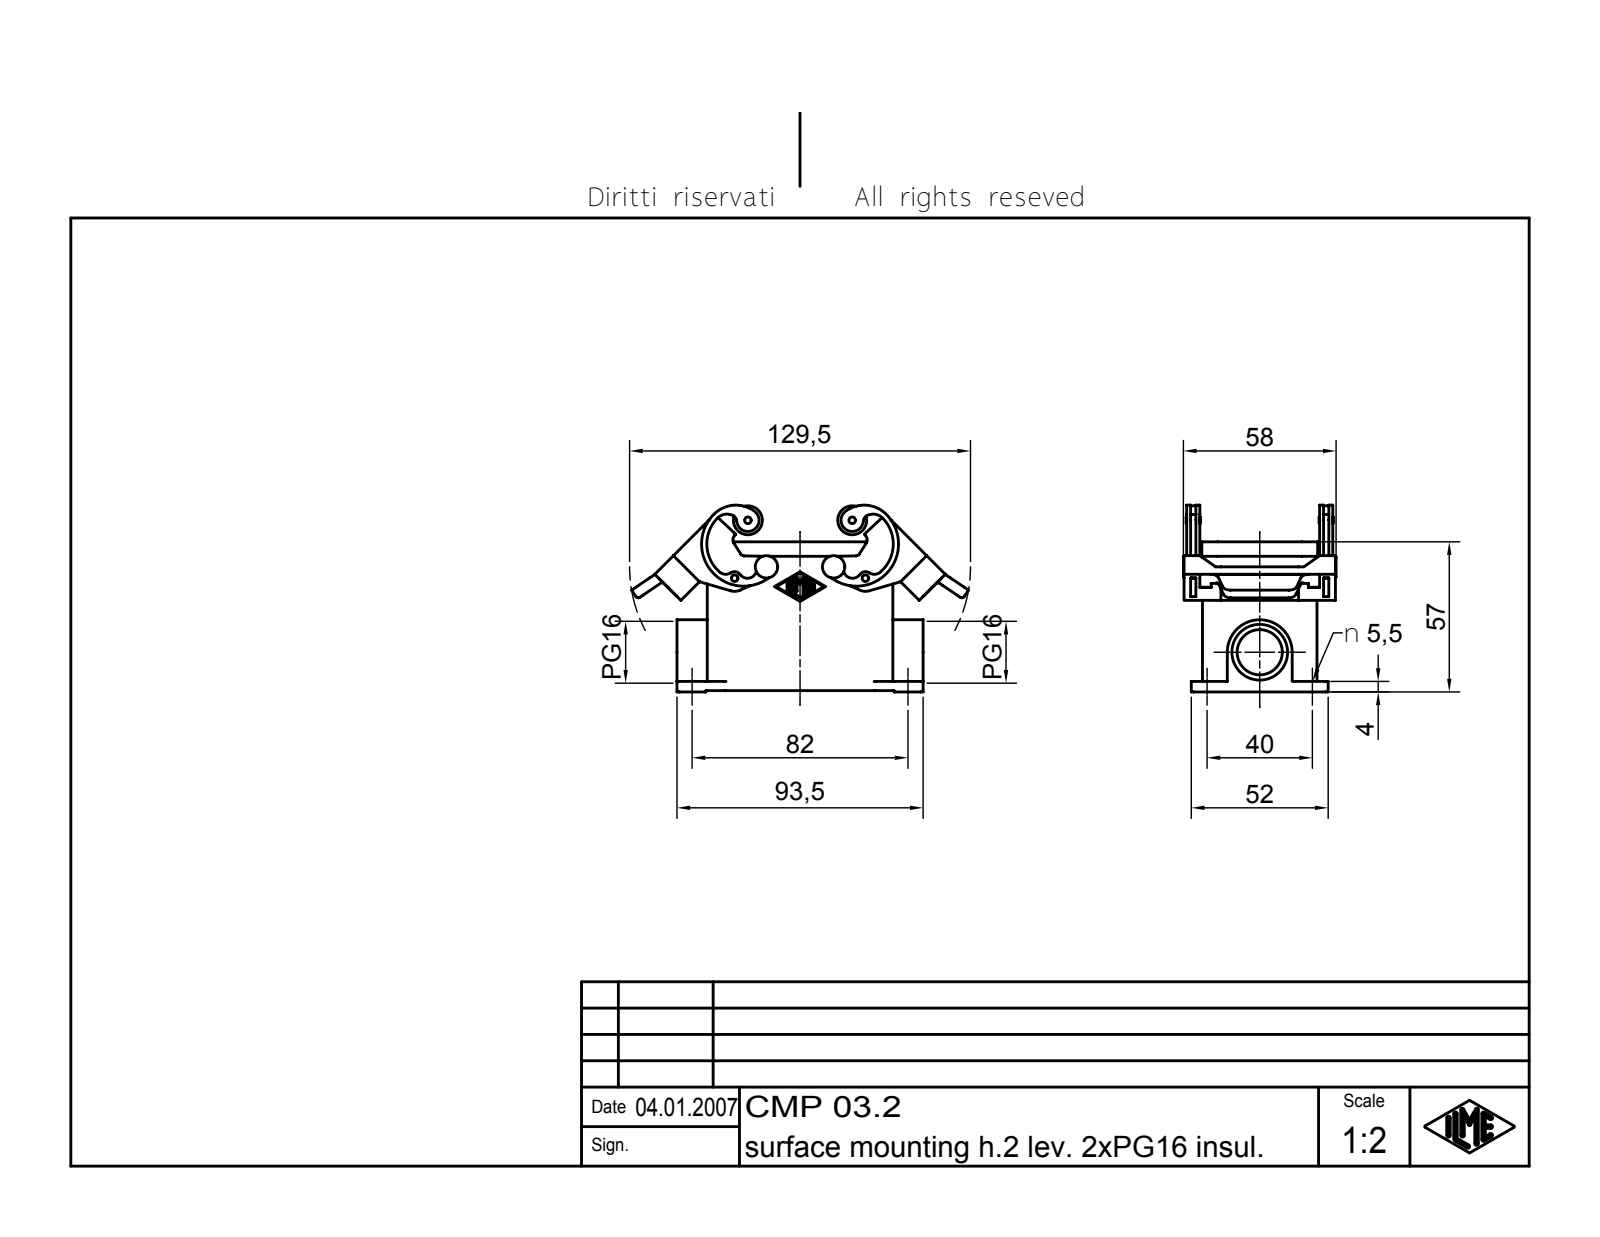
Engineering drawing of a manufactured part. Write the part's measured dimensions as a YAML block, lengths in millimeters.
part_name: "CMP 03.2"
step_written_by: "Autodesk Inventor 7 (AUTOMOTIVE_DESIGN)"
units: millimeters
bodies: {solids: 1, faces: 748, planar: 191, cylindrical: 205, other: 352}
overall_size: [127.99, 70.94, 58]
volume: 87424
surface_area: 50733
round_holes:
  - {diameter: 2, count: 4}
  - {diameter: 5.5, count: 4}
  - {diameter: 2.5, count: 2}
  - {diameter: 17.16, count: 1}
  - {diameter: 21.16, count: 1}
round_bosses_or_shafts:
  - {diameter: 11, count: 2}
  - {diameter: 5, count: 2}
  - {diameter: 3, count: 2}
partial_cylinders:
  - {radius: 1, count: 20}
  - {radius: 0.38, count: 14}
  - {radius: 3, count: 12}
  - {radius: 6, count: 8}
  - {radius: 2.5, count: 6}
  - {radius: 1.5, count: 4}
  - {radius: 2, count: 4}
  - {radius: 3.5, count: 4}
face_to_face_distances: [3, 40.5, 3.5, 43.5, 4, 37.5, 50.5, 56.5, 0.75, 4.5]
hole_center_spacings: [22.56, 40, 49.78, 82, 91.24, 39.64, 49.68]
